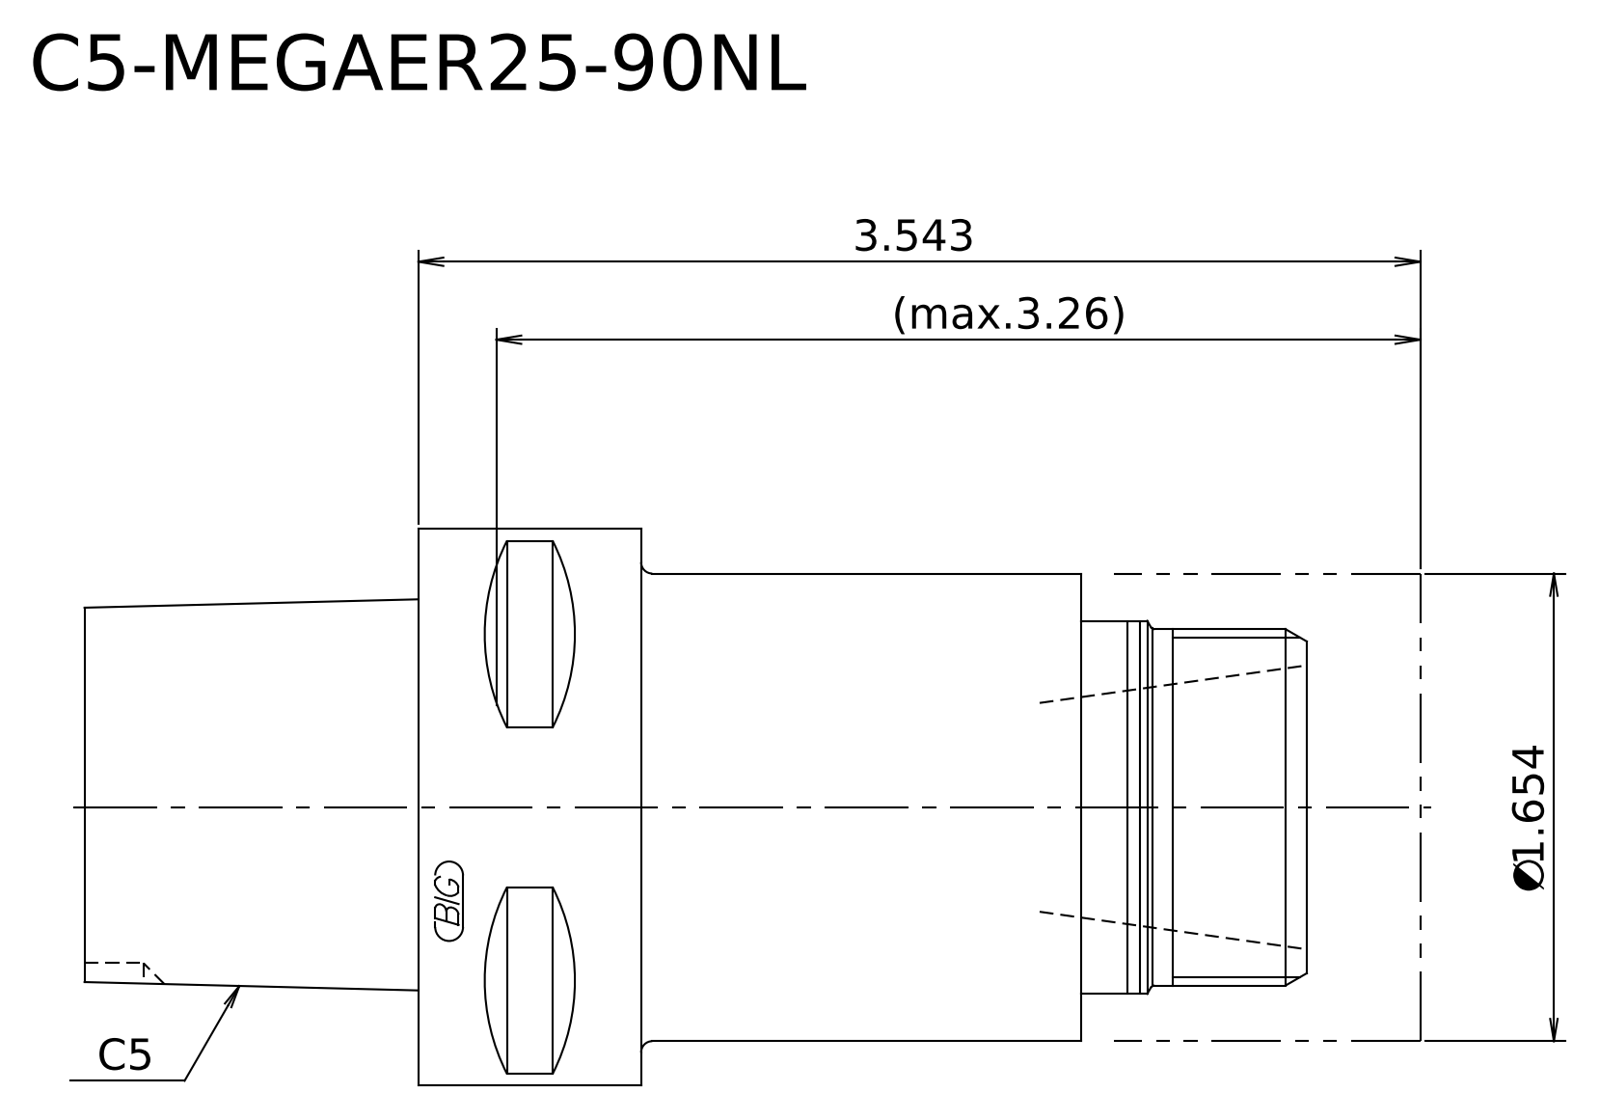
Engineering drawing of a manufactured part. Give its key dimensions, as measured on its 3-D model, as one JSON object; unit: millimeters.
{"step_written_by": "Kubotek KeyCreator 2011 V10.0.2 (22737) (automotive_design)", "units": "millimeters", "bodies": {"solids": 2, "faces": 16, "planar": 7, "cylindrical": 5, "other": 4}, "overall_size": [120, 50, 50], "volume_mm3": 176049, "surface_area_mm2": 23718, "round_bosses_or_shafts": [[50, 1], [42, 1], [33.5, 1], [32, 1]], "face_to_face_distances": [27.5, 90, 62.5, 120, 92.5, 30, 10.2, 17.3, 79.8, 109.8]}
